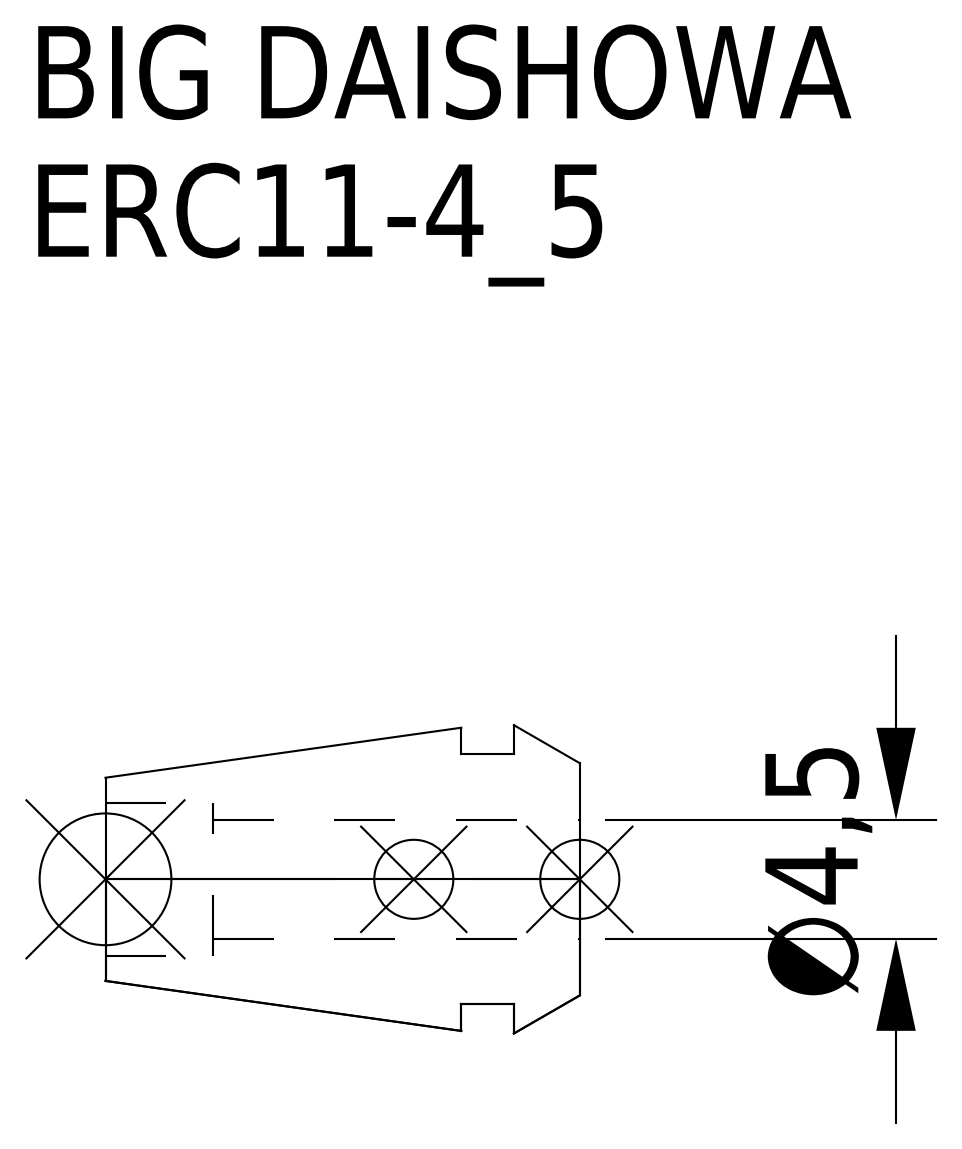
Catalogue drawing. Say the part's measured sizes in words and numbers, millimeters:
The part is named "ERC11-4_5". Its 3-D file was written by "CREO PARAMETRIC BY PTC INC, 2016380 (AUTOMOTIVE_DESIGN)". It is 1 solid with 15 faces: 5 planar, 6 cylindrical and 4 other. Overall it measures 18 by 11.7 by 11.7 millimeters. Its volume is 1 012 cubic millimeters and its surface area 981 square millimeters. Round holes: 1 of diameter 4.5, 1 of diameter 5.8. Round bosses or shafts: 1 of diameter 9.5. The main face-to-face distances are 2.5, 4.5, 2, 18, 15.5, 13.5, 13.93, 11.43, 9.43, 4.07.
